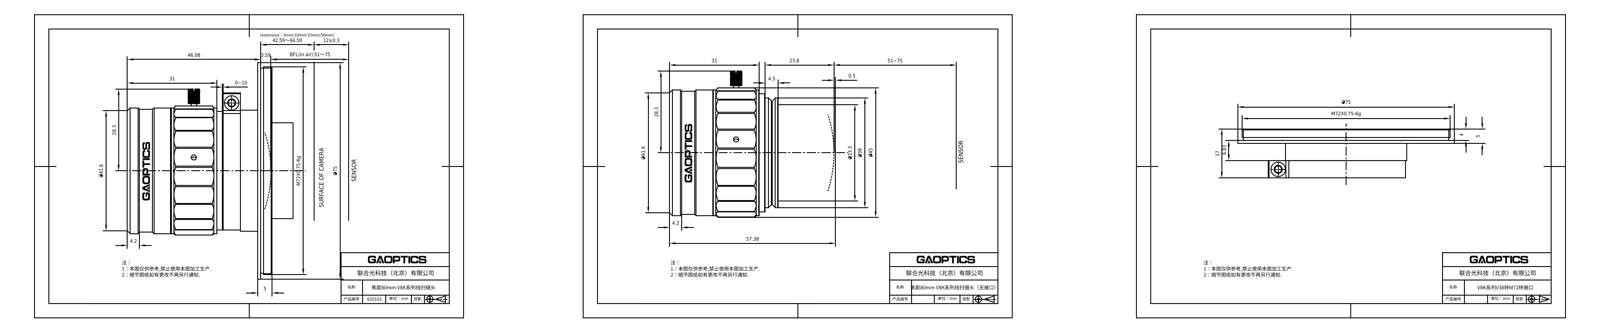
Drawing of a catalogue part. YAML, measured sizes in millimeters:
part_name: "620101"
step_written_by: "SolidWorks 2019 (CONFIG_CONTROL_DESIGN)"
units: millimeters
bodies: {solids: 4, faces: 1422, planar: 0, cylindrical: 0, other: 1422}
overall_size: [75, 75, 57.38]
volume: 77988
surface_area: 30999
